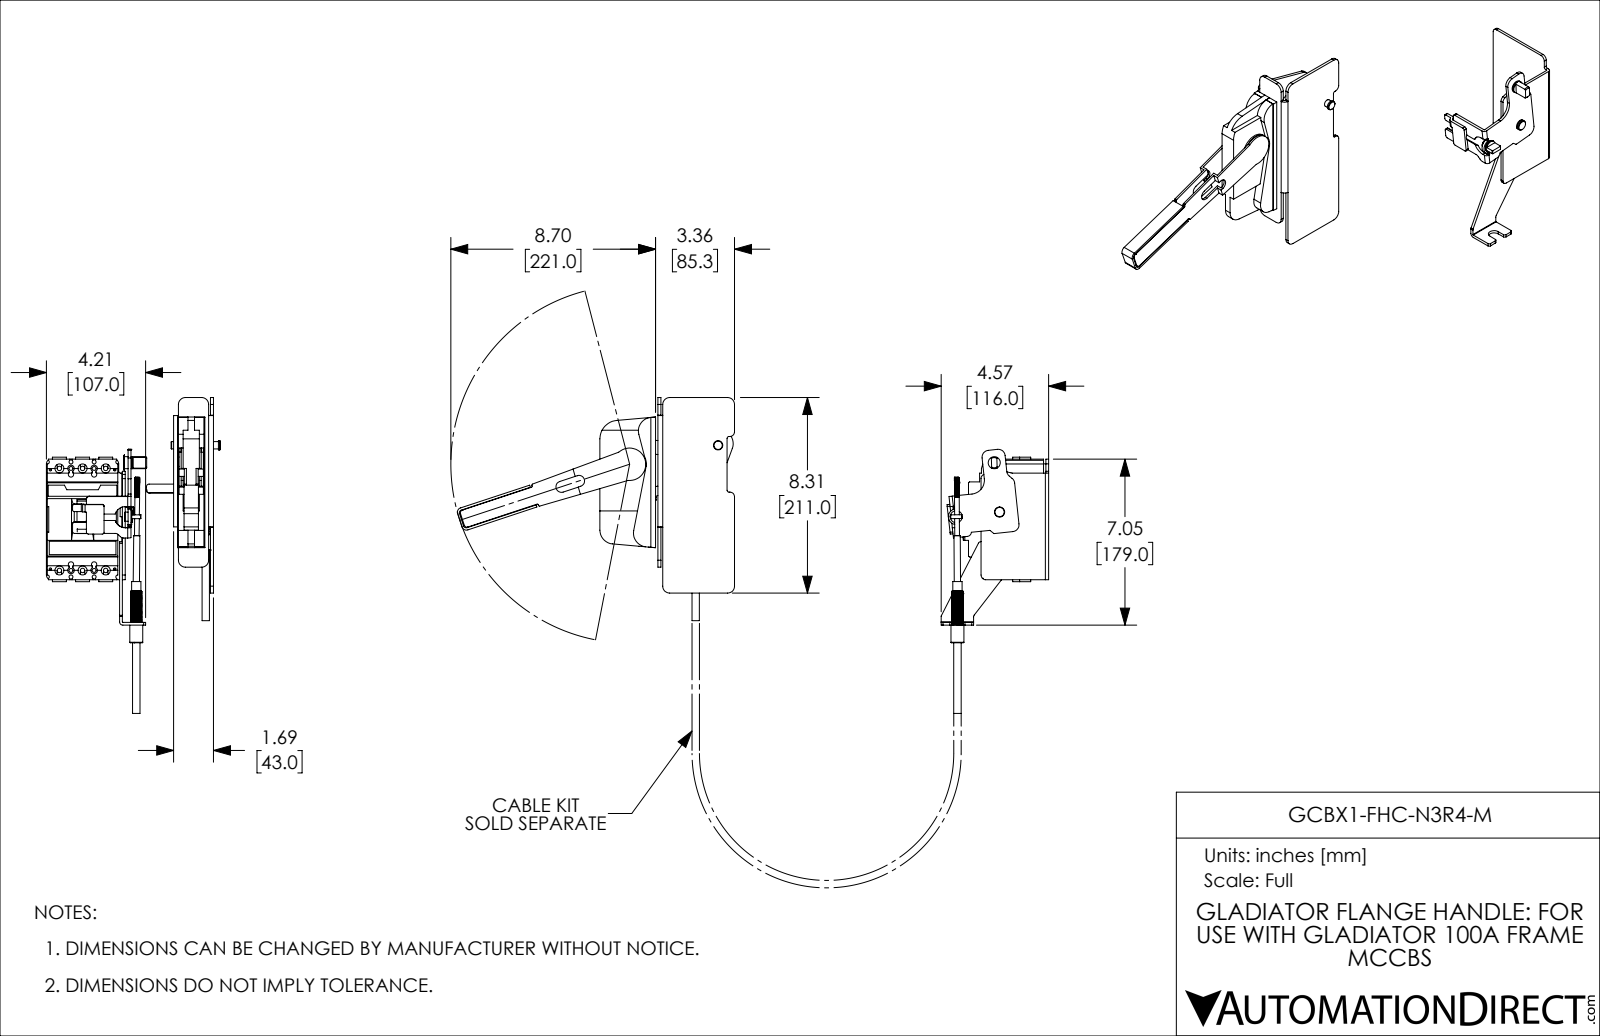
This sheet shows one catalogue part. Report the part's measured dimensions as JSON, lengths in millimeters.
{"part_name": "GCBX1-FHC-N3R4-M_2; GCB100S-3FF15LL; GCBX1-FHC-N3R4-M_1; GCBX2-CBL-36_2 (+2 more)", "step_written_by": "SolidWorks 2021 (CONFIG_CONTROL_DESIGN)", "units": "millimeters", "bodies": {"solids": 29, "faces": 2036, "planar": 1080, "cylindrical": 781, "other": 175}, "overall_size": [638.3, 340.7, 187.6], "volume_mm3": 1111000, "surface_area_mm2": 310800, "round_holes": [[4.2, 8], [4.8, 6], [9.7, 6], [2.5, 4], [7, 4], [5.1, 2], [8, 2], [3, 1], [6.2, 1], [6.5, 1], [11, 1], [13, 1]], "round_bosses_or_shafts": [[10, 5], [7.3, 2], [6.7, 2], [5, 2], [35, 1], [14, 1], [13, 1], [12, 1]], "partial_cylinders_radius": [[0.3, 86], [0.5, 39], [7.5, 20], [1, 18], [3, 18], [5, 17], [2, 16], [4, 14]], "face_to_face_distances": [3.2, 3, 5, 9.2, 92.1, 95.1, 98.3, 81, 76, 176.1], "hole_center_spacings": [12.5, 14.3, 25, 110.7, 117.7, 112.8, 110, 7]}
